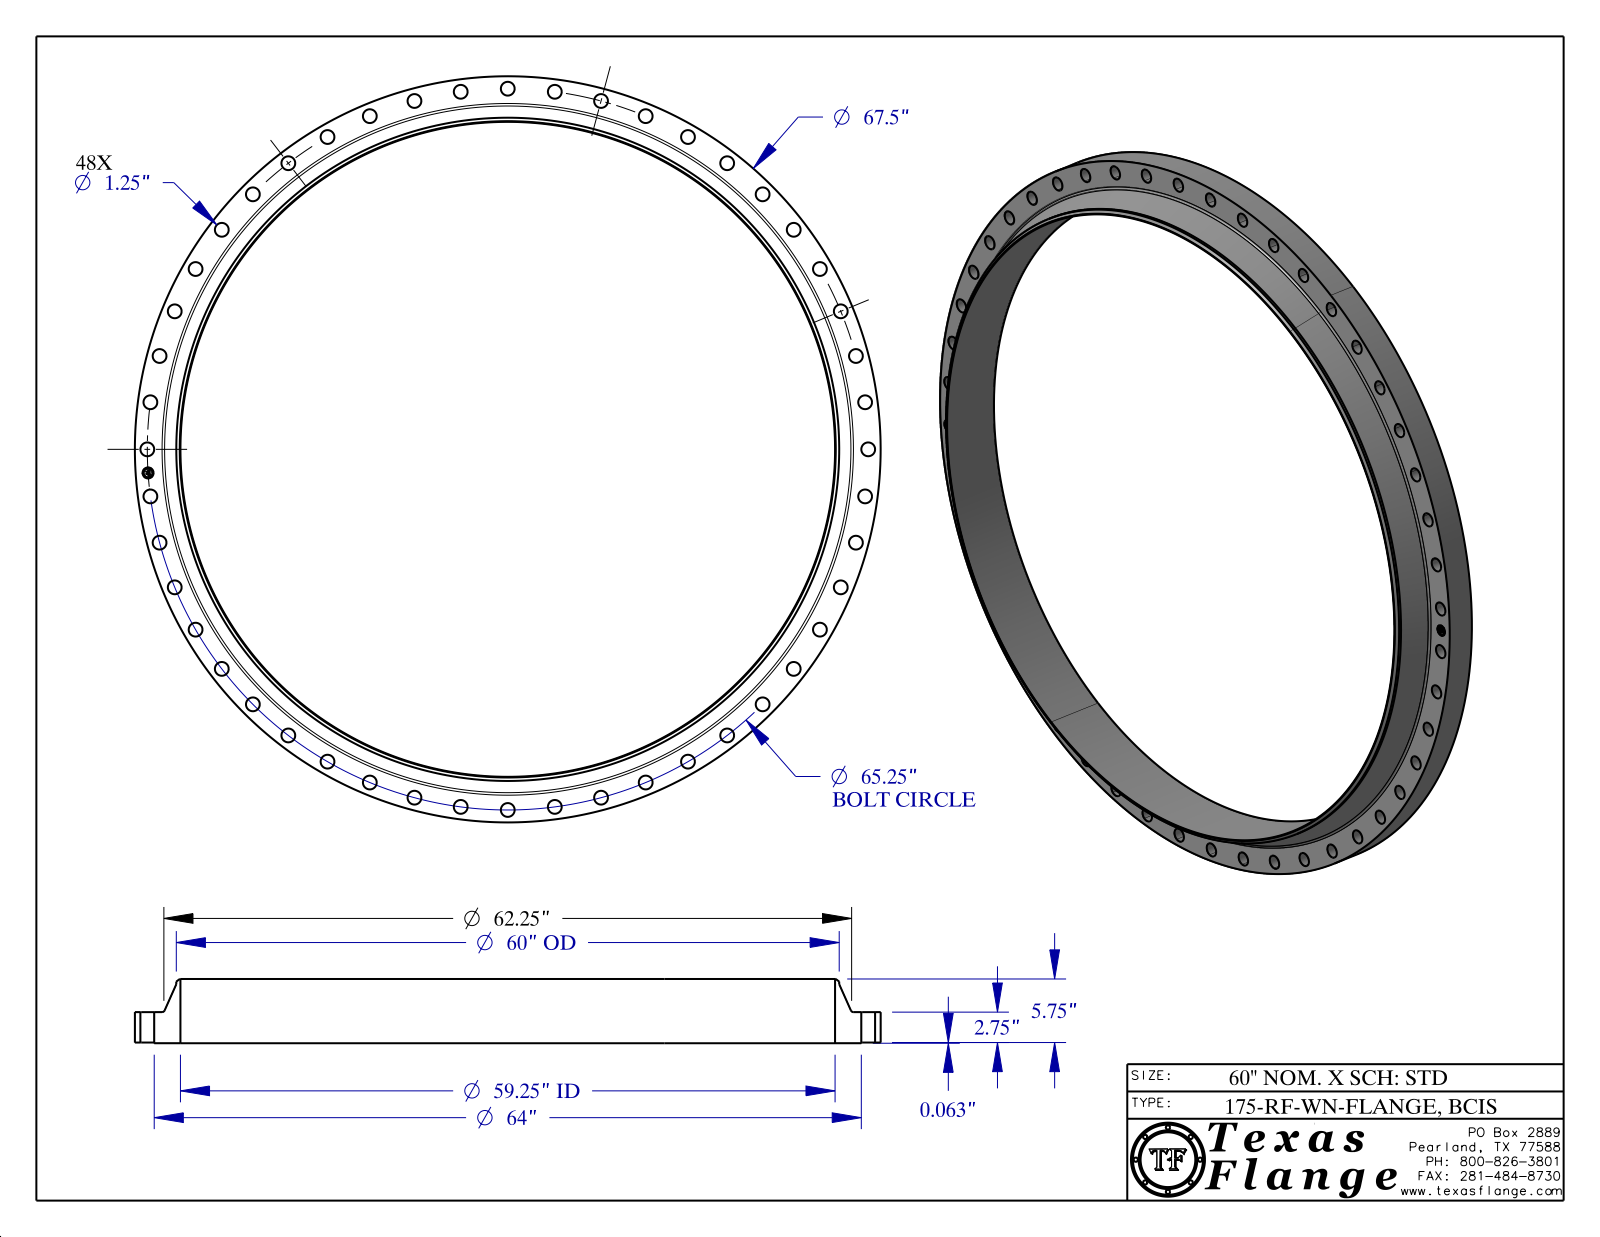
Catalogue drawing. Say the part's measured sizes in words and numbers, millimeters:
The part is named "175-RF-WN, BCIS". Its 3-D file was written by "CATIA V5 STEP AP214 (AUTOMOTIVE_DESIGN)". It is 1 solid with 499 faces: 369 planar, 124 cylindrical and 6 other. Overall it measures 1714.5 by 1714.5 by 147.7 millimeters. Its volume is 42 620 000 cubic millimeters and its surface area 2 637 000 square millimeters. Round holes: 48 of diameter 31.8, 1 of diameter 25.4, 1 of diameter 1505. Round bosses or shafts: 8 of diameter 1.5, 1 of diameter 1714.5, 1 of diameter 1625.6, 1 of diameter 1524, 1 of diameter 20. The main face-to-face distances are 71.5, 1.6, 69.9, 147.7, 146.1, 76.2, 71.1, 69.5, 0.4, 76.6. The hole center spacings are 828.7, 828.7, 1378.1, 216.3, 1008.9, 532.7, 1600.9, 429.
